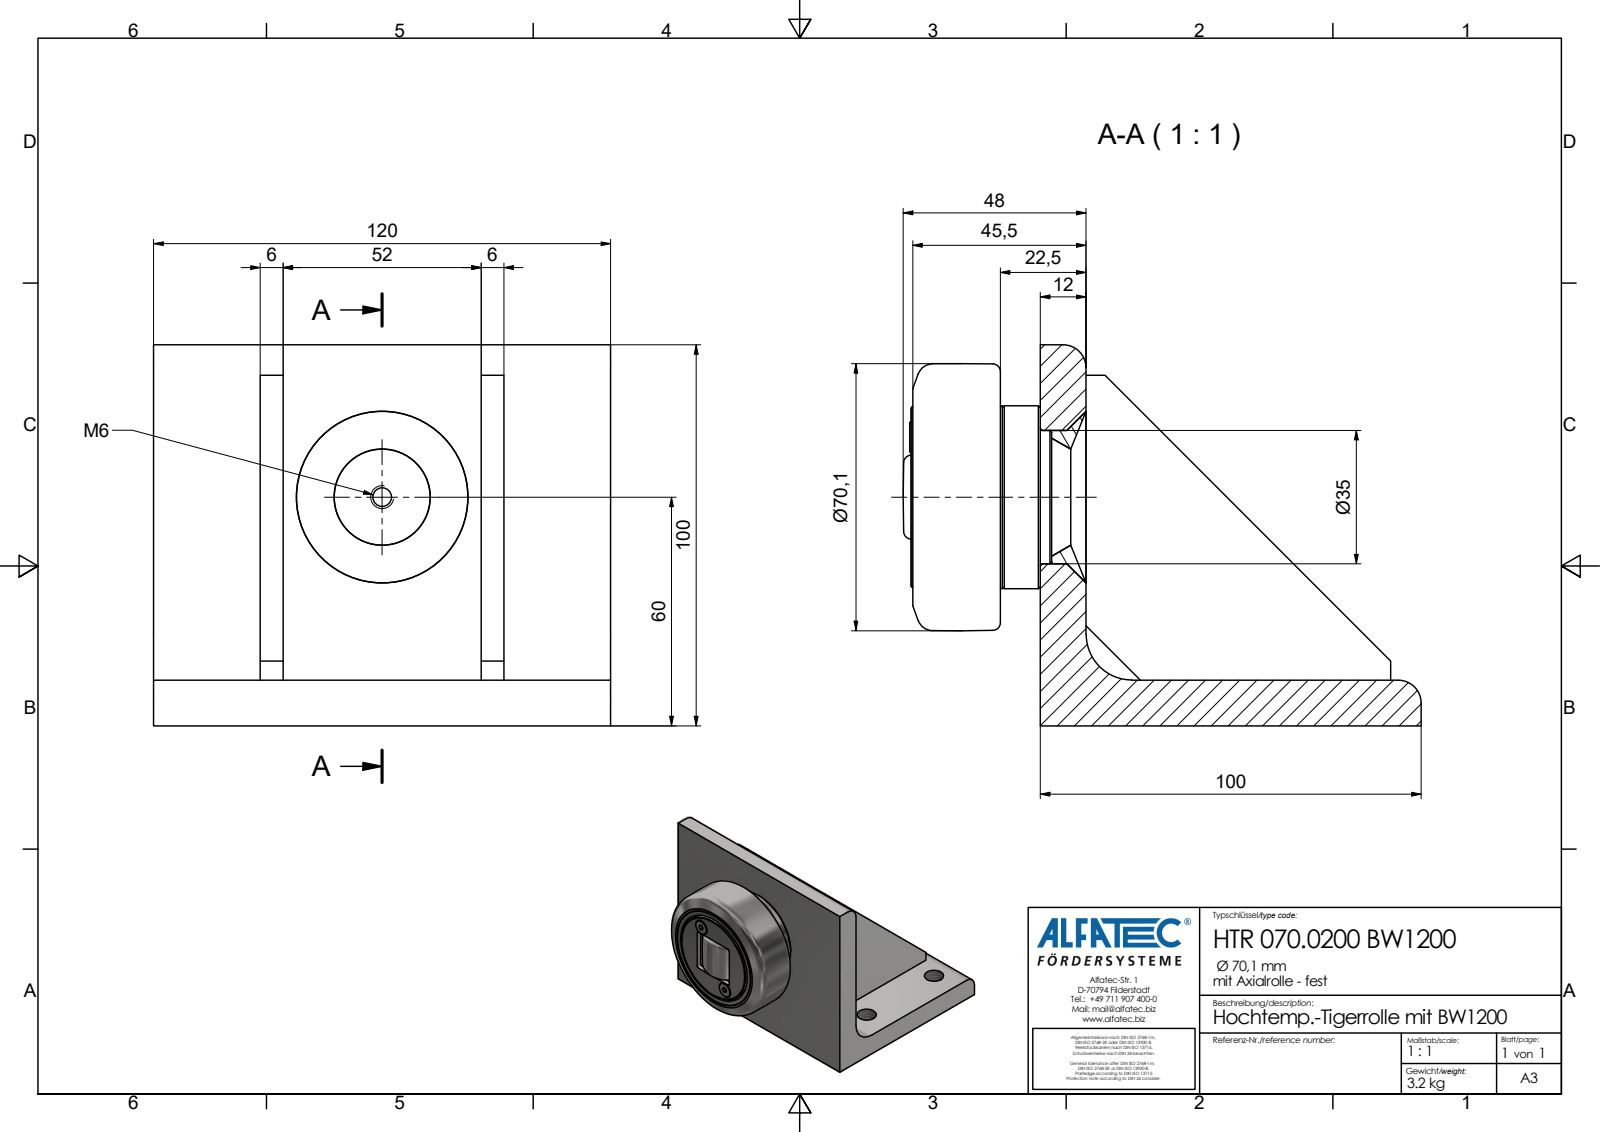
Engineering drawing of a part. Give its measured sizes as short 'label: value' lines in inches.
name: HTR 070.0200 BW1200_Kontur
written by: Autodesk Inventor 2020 (AP242_MANAGED_MODEL_BASED_3D_ENGINEERING_MIM_LF)
unit: in
bodies: 1 solid, 81 faces (50 planar, 18 cylindrical, 13 other)
size: 5.354 × 4.724 × 3.937
volume: 25.2 in³; area: 119.2 in²
holes: 4× ⌀0.398, 1× ⌀0.098, 1× ⌀0.194
bosses: 2× ⌀0.307, 1× ⌀1.89, 1× ⌀1.862
rounds: 4× R0.039, 2× R0.236, 1× R0.472
face distances: 0.472, 0.236, 2.283, 1.339, 3.622, 1.102, 3.386, 2.52, 2.047, 4.724
hole spacings: 1.969, 3.543, 4.054
